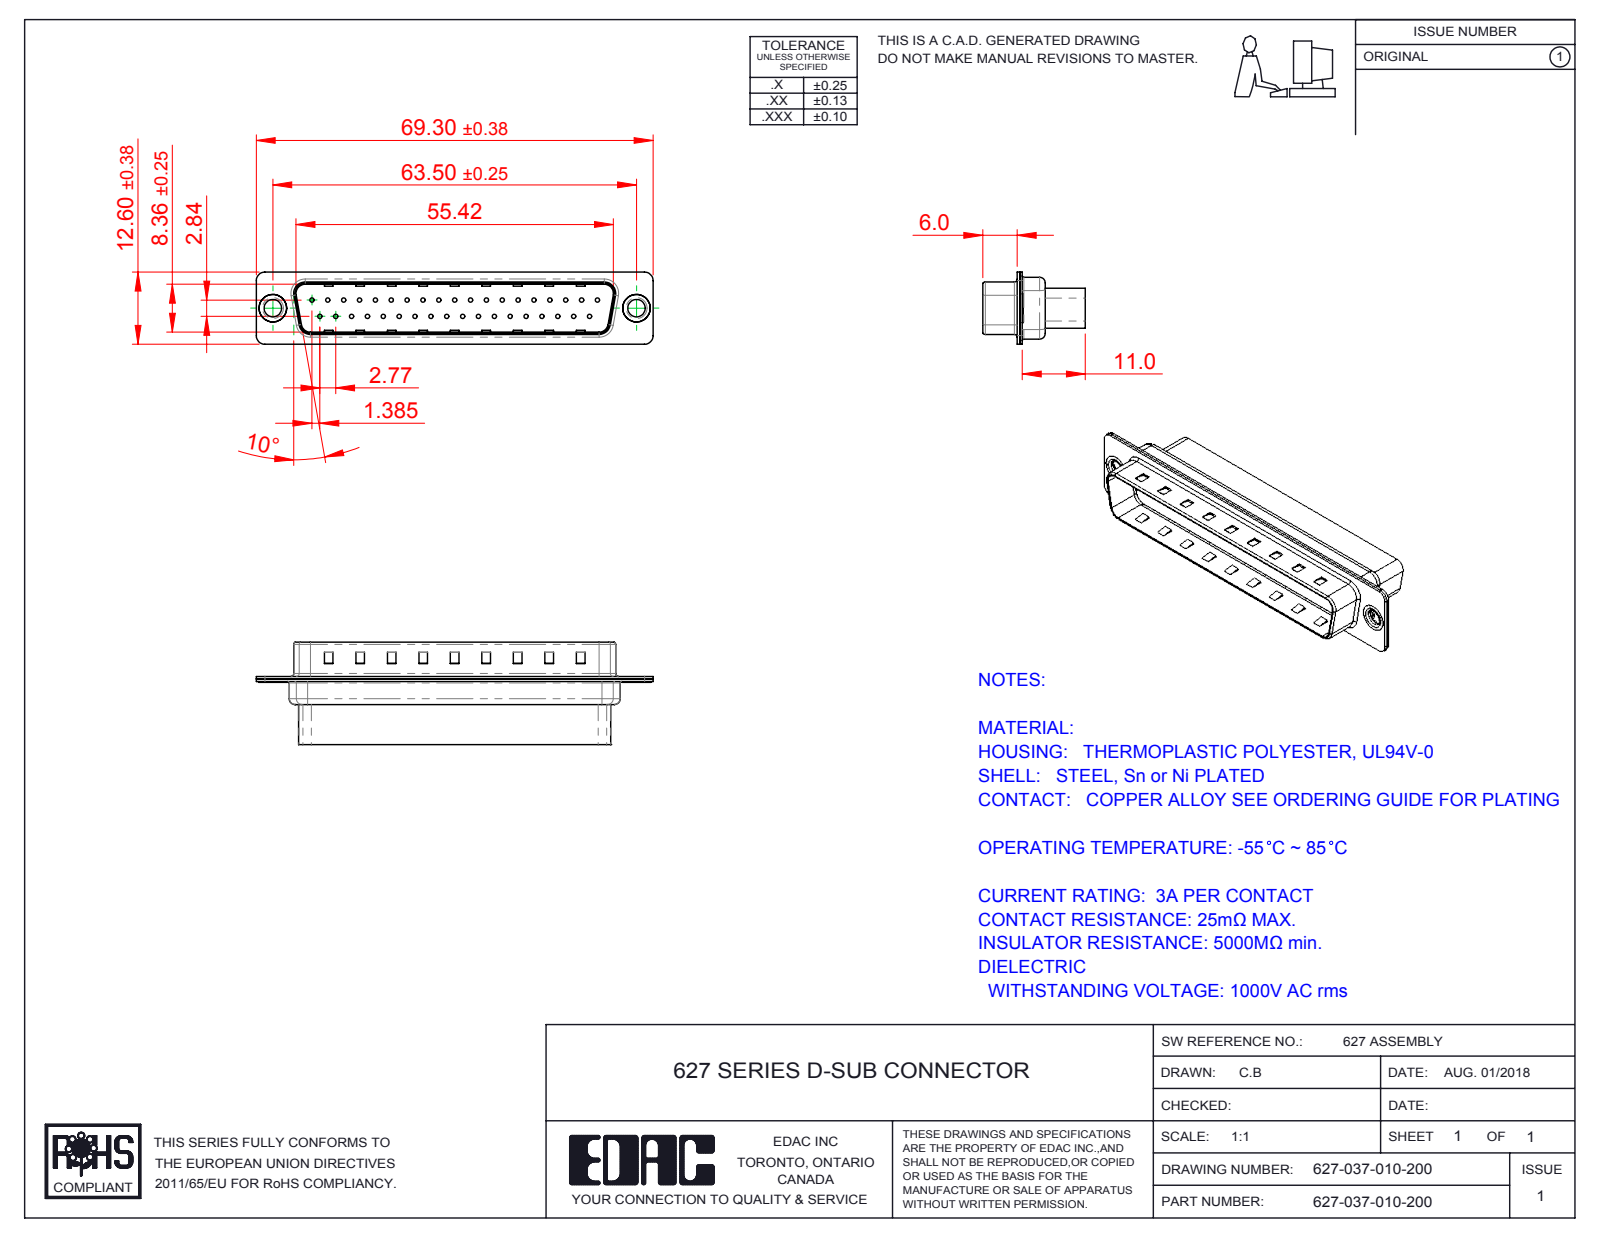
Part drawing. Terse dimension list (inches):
name: 627 Housing_37 HP; 627-037-010-200; 627 Shell Front_37 Contacts; 627 Thru Hole Rivet (+1 more)
written by: SolidWorks 2016 (CONFIG_CONTROL_DESIGN)
unit: in
bodies: 5 solids, 682 faces (277 planar, 347 cylindrical, 58 other)
size: 2.728 × 0.705 × 0.496
volume: 0.302 in³; area: 13.78 in²
holes: 37× ⌀0.03, 37× ⌀0.063, 37× ⌀0.079, 2× ⌀0.12, 2× ⌀0.157, 2× ⌀0.189
bosses: 2× ⌀0.197, 2× ⌀0.193, 2× ⌀0.14
rounds: 16× R0.059, 12× R0.079, 8× R0.02, 8× R0.063, 4× R0.01, 4× R0.024, 4× R0.026, 4× R0.035
face distances: 0.016, 0.032, 0.377, 0.027, 0.302, 0.018, 0.043, 0.318, 0.345, 0.276
hole spacings: 0.124, 0.109, 0.218, 0.327, 0.198, 0.398, 0.436, 0.503
